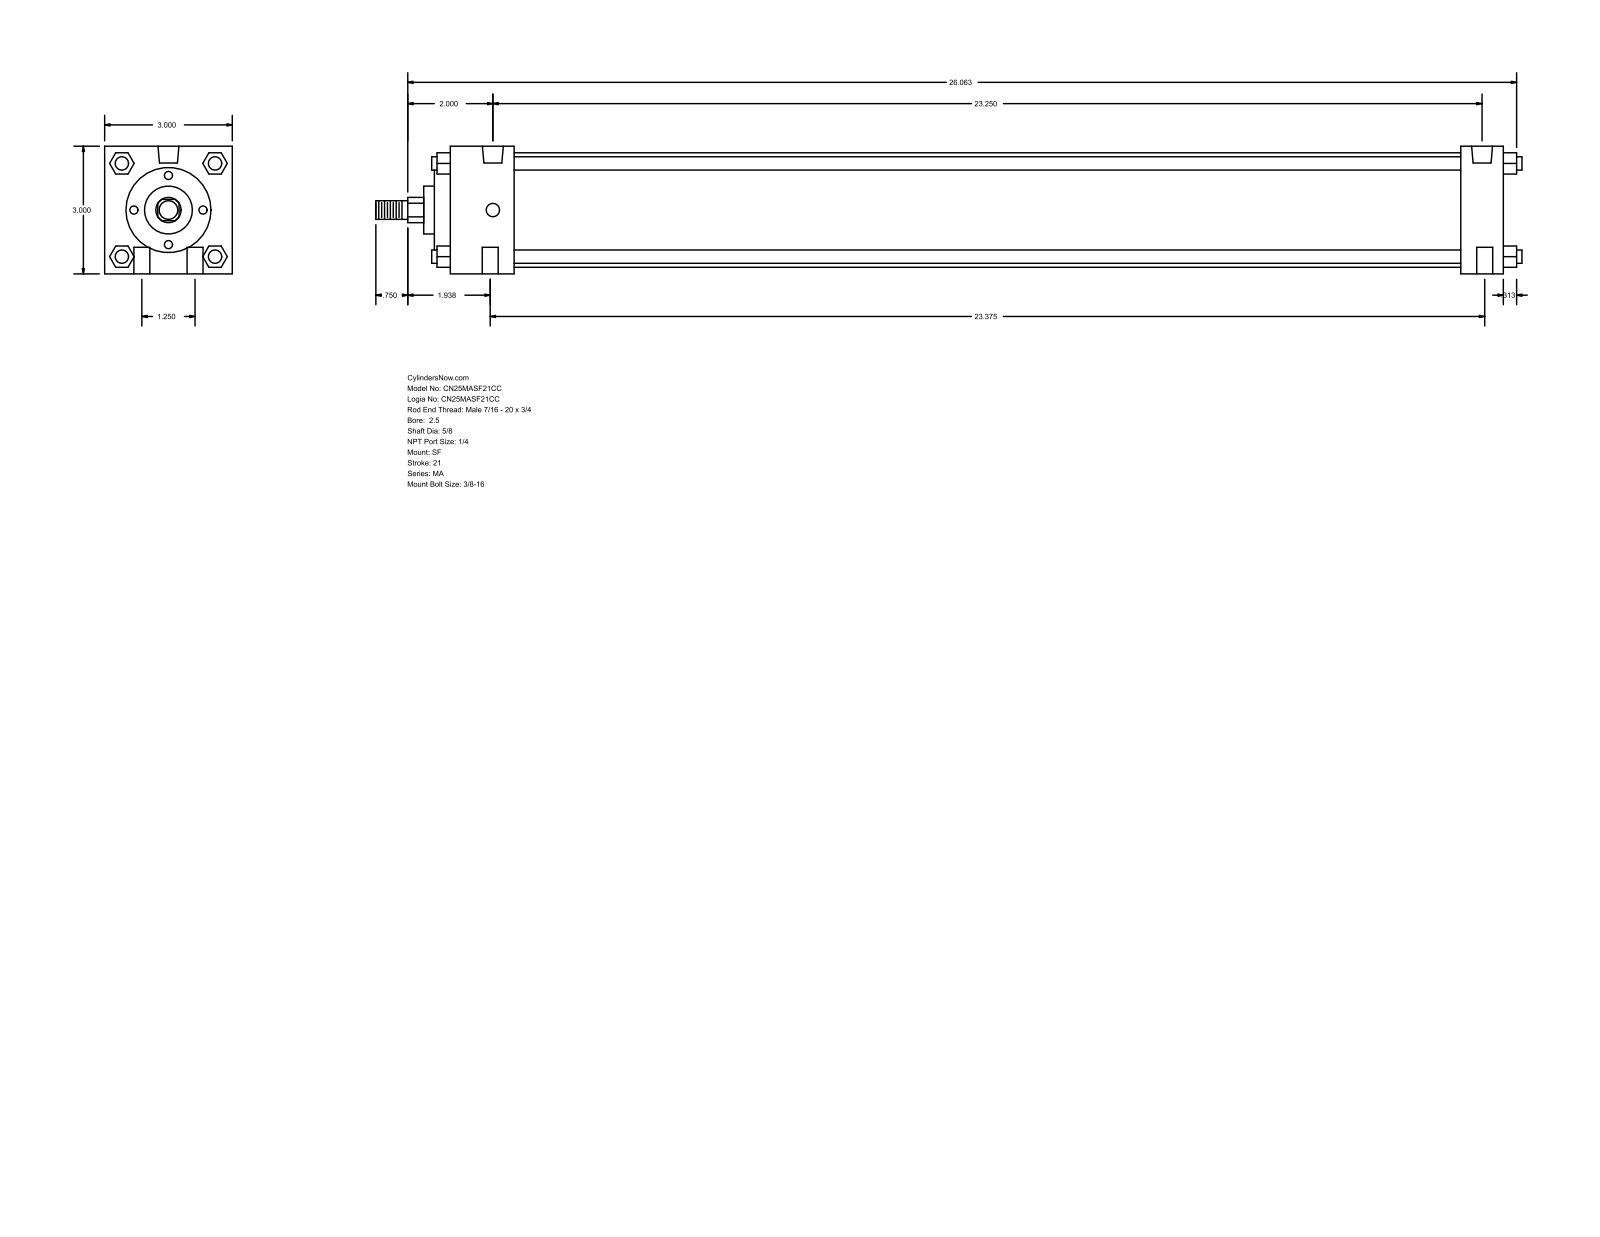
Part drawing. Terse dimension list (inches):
name: MA_SF__0250_0.625
written by: GSSL Pune (CONFIG_CONTROL_DESIGN)
unit: in
bodies: 0 solids, 126 faces (95 planar, 31 cylindrical, 0 other)
size: 26.937 × 3 × 3
holes: 4× ⌀0.375, 2× ⌀0.313, 2× ⌀0.492
bosses: 4× ⌀0.313, 1× ⌀2.69, 1× ⌀2, 1× ⌀1.125, 1× ⌀0.625, 1× ⌀0.437
rounds: 1× R0.297
face distances: 3, 24.75, 1, 23.75, 1.5, 22.25, 23.25, 0.5, 0.375, 1.875
hole spacings: 0.628, 23.321, 1.25, 23.25, 23.375, 23.409
